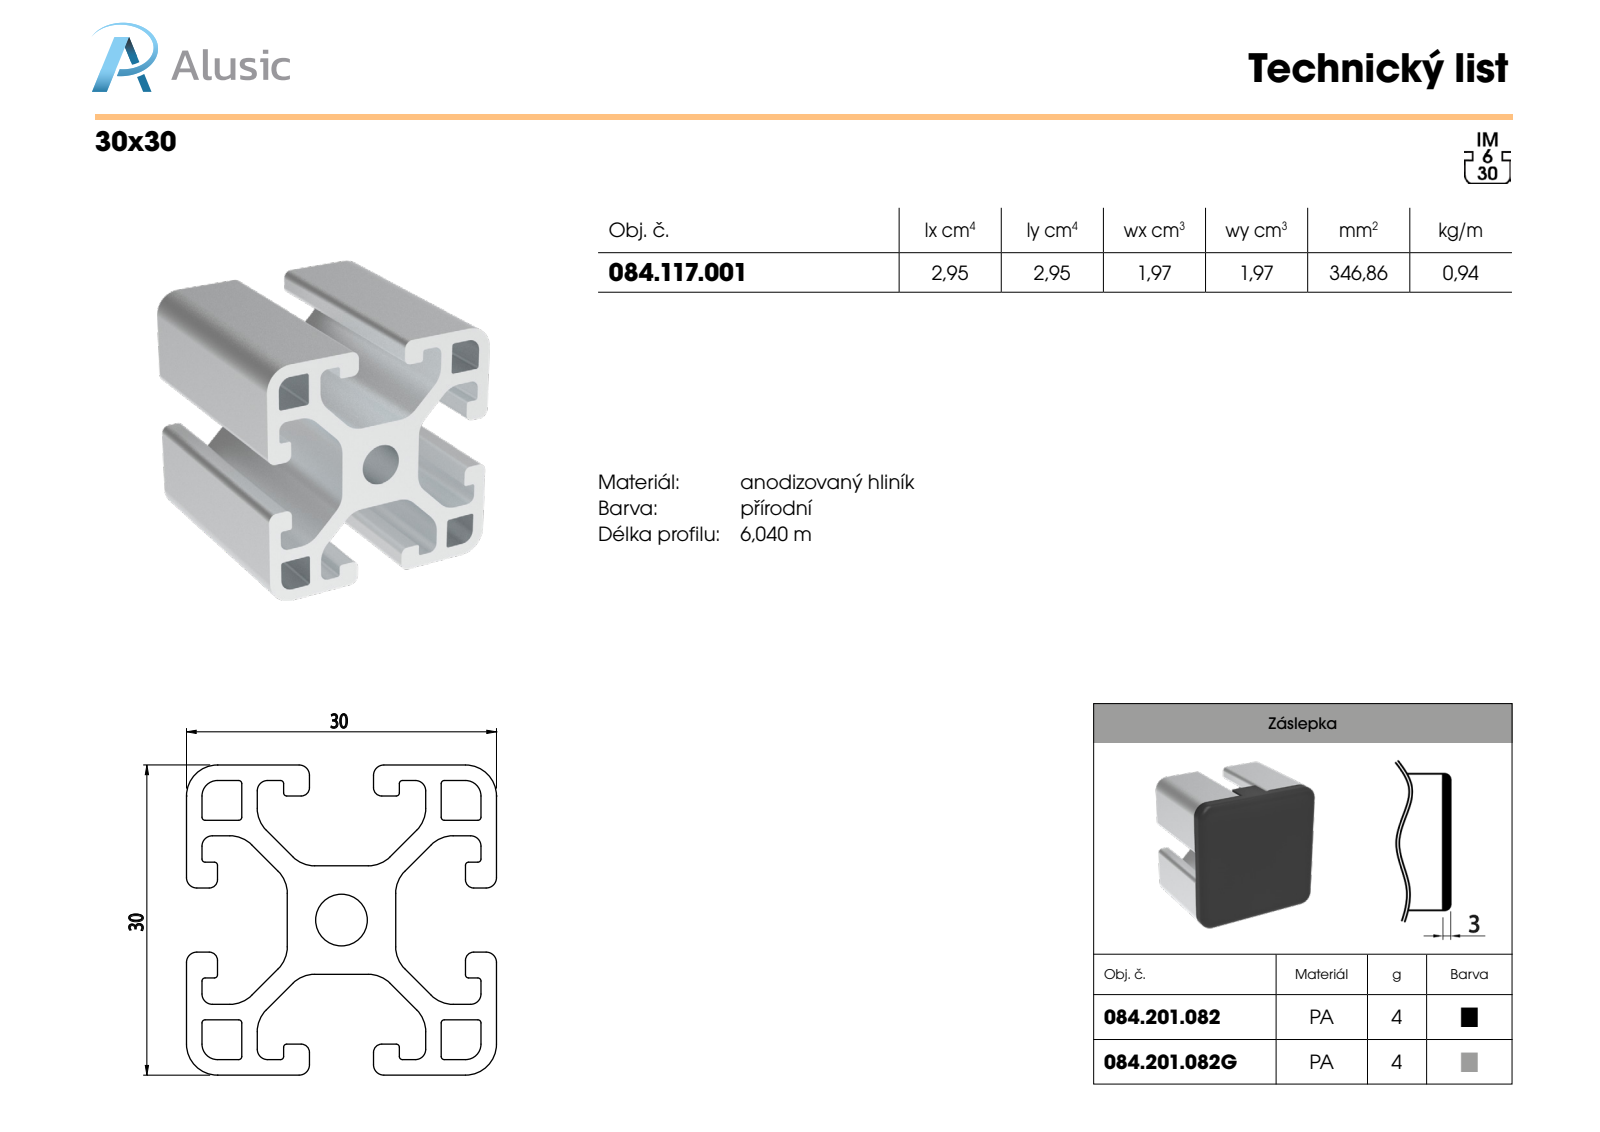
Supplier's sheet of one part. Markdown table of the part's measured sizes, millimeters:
| quantity | value |
| --- | --- |
| part name | 084.201.086 |
| STEP written by | SolidWorks 2018 (AUTOMOTIVE_DESIGN) |
| units | millimeters |
| bodies | 1 solid, 100 faces (30 planar, 33 cylindrical, 37 other) |
| overall size | 30 × 30 × 9 |
| volume | 2 181 mm³ |
| surface area | 2 433 mm² |
| round holes (diameter × count) | 8 × 1 |
| round bosses / shafts (diameter × count) | 10 × 1 |
| partial cylindrical surfaces (radius × count) | 0.3 × 8, 0.5 × 4, 1.5 × 4, 3 × 4, 2.55 × 1 |
| main face-to-face distances | 2, 1, 3, 2.5, 27.5, 14.4, 15.6, 13.1, 11.9, 30 |
